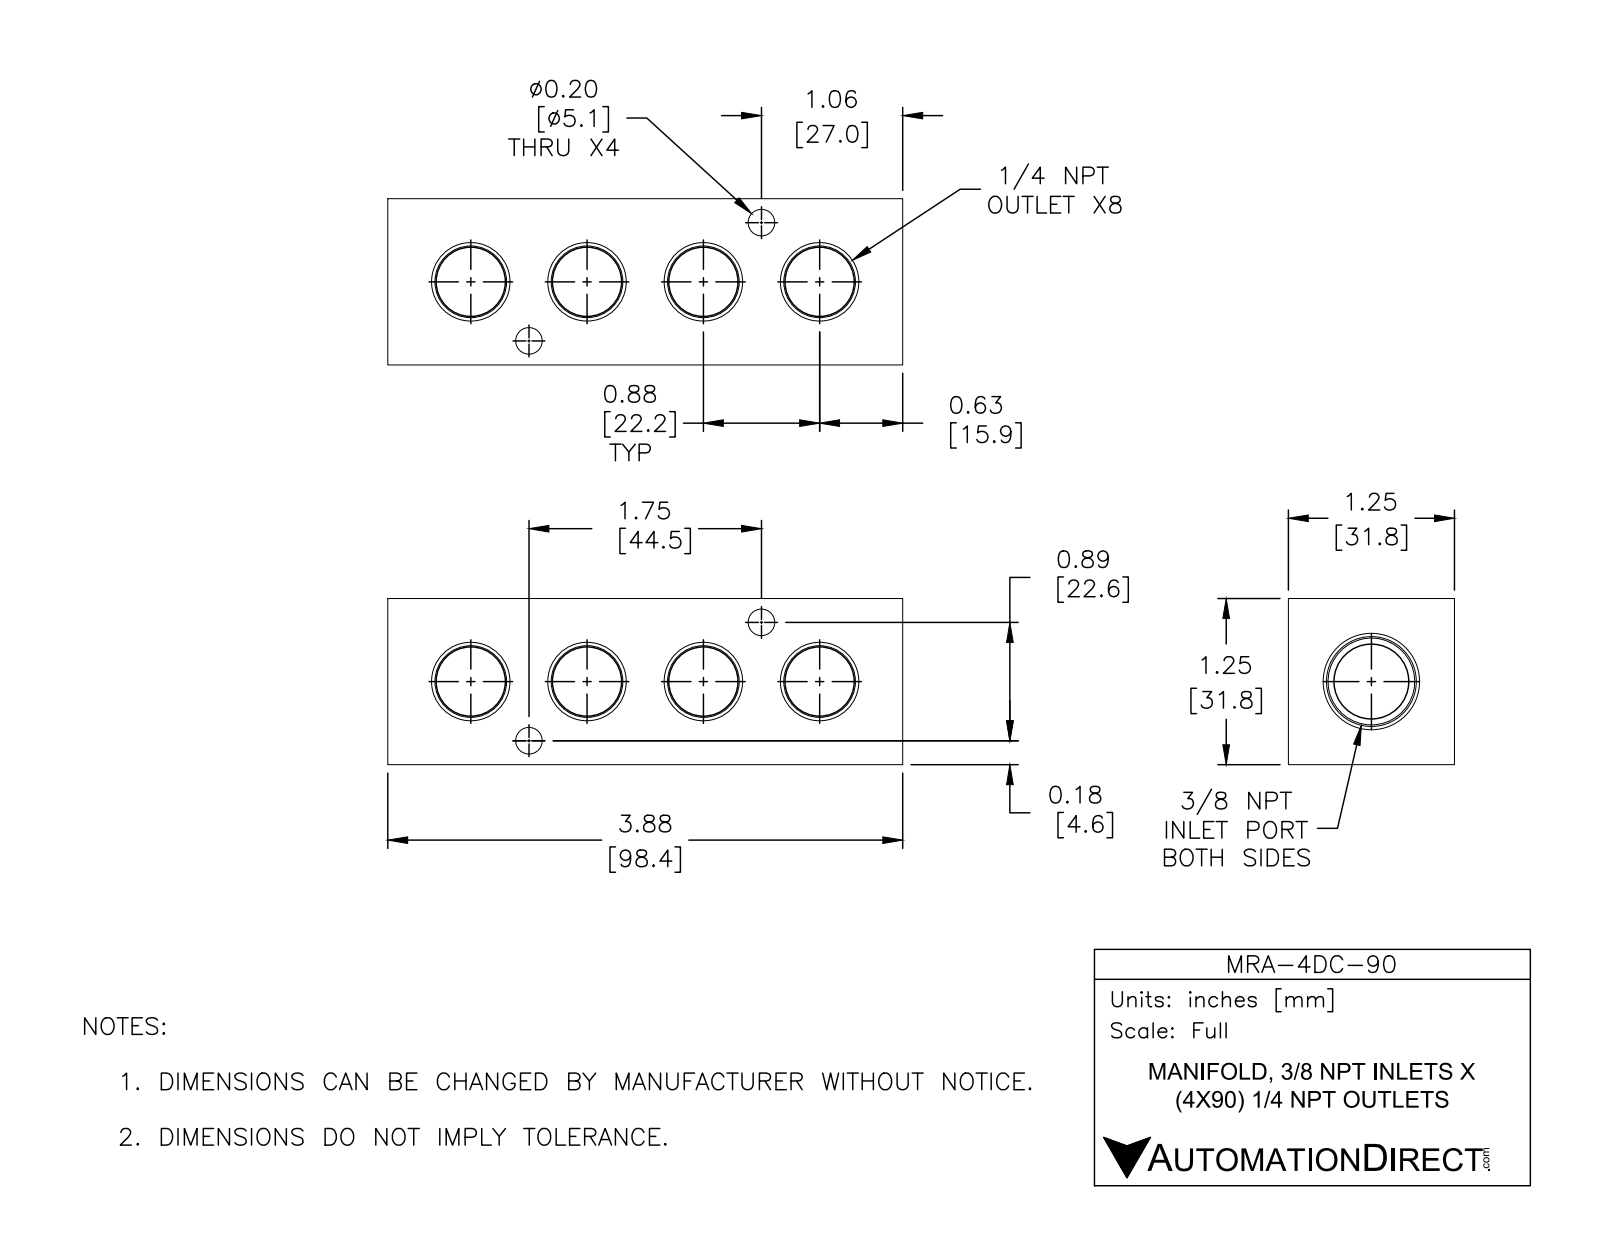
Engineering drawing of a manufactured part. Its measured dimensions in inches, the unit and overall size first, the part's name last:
Units: inches
Overall size (bounding box): 3.875 × 1.25 × 1.25
Round holes (diameter × count): ⌀0.2 ×4, ⌀0.562 ×1
Partial cylindrical surfaces — rounded edges, fillets, slot ends (radius × count): R0.219 ×8
Main face-to-face distances: 1.25, 3.875, 0.86, 0.39, 0.41, 3.465, 3.055
Hole centre spacings: 1.963
Volume: 4.209 in³ · Surface area: 33.3 in²
Bodies: 1 solid, 102 faces (26 planar, 36 cylindrical, 40 other)
Part name (STEP PRODUCT): MRA-4DC-90
STEP written by: SolidWorks 2015 (CONFIG_CONTROL_DESIGN)
